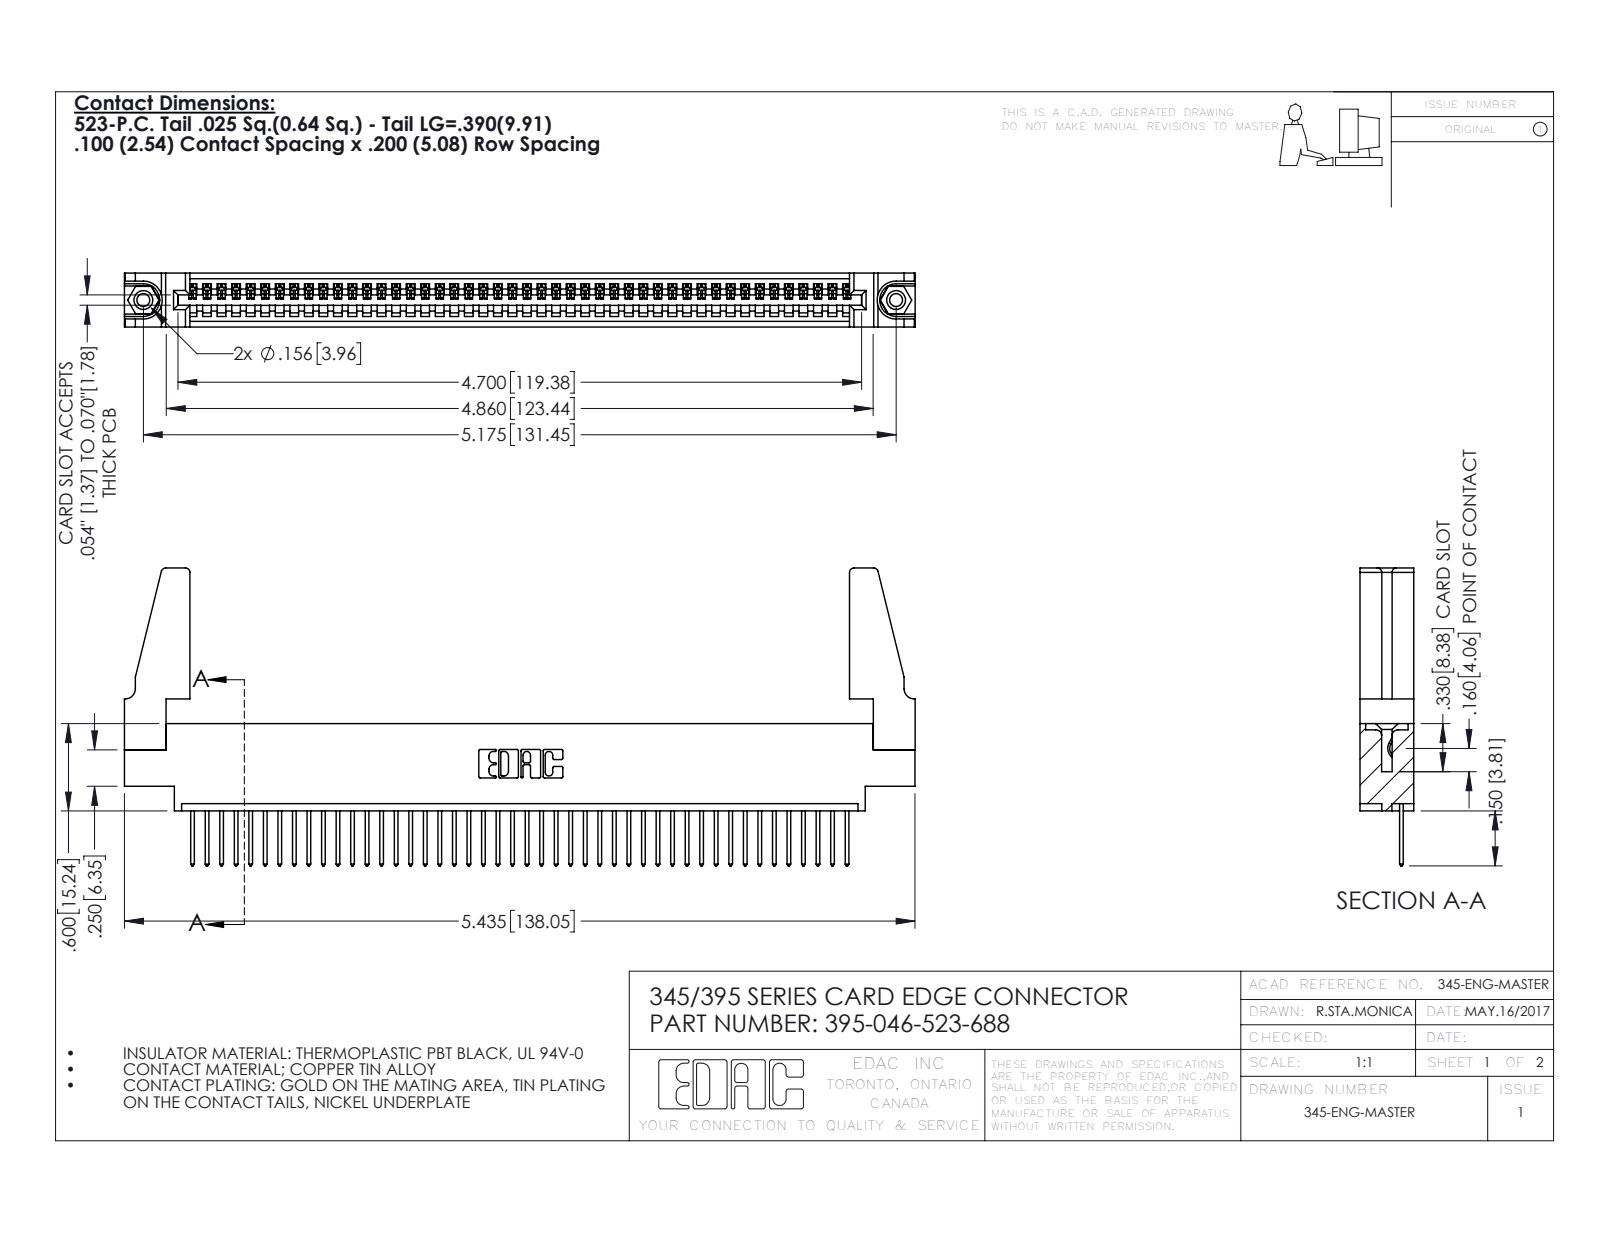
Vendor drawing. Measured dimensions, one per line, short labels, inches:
name: 345-220-078_345-220-088; 395-046-523-688; 345-292-001_345-293-123; 345 Part_0.170 Offset - 0.156 Dia-TH (+1 more)
written by: SolidWorks 2016 (CONFIG_CONTROL_DESIGN)
unit: in
bodies: 51 solids, 2922 faces (1996 planar, 910 cylindrical, 16 other)
size: 5.436 × 2.047 × 0.37
volume: 0.993 in³; area: 32.02 in²
holes: 2× ⌀0.089, 2× ⌀0.125, 2× ⌀0.156, 1× ⌀0.064
bosses: 2× ⌀0.155
rounds: 92× R0.006, 92× R0.01, 22× R0.01, 8× R0.03, 6× R0.007, 6× R0.031, 3× R0.026, 2× R0.031
face distances: 0.072, 0.298, 0.37, 0.098, 0.272, 0.025, 0.2, 0.225, 0.175, 0.149
hole spacings: 0.27, 4.939, 5.175
